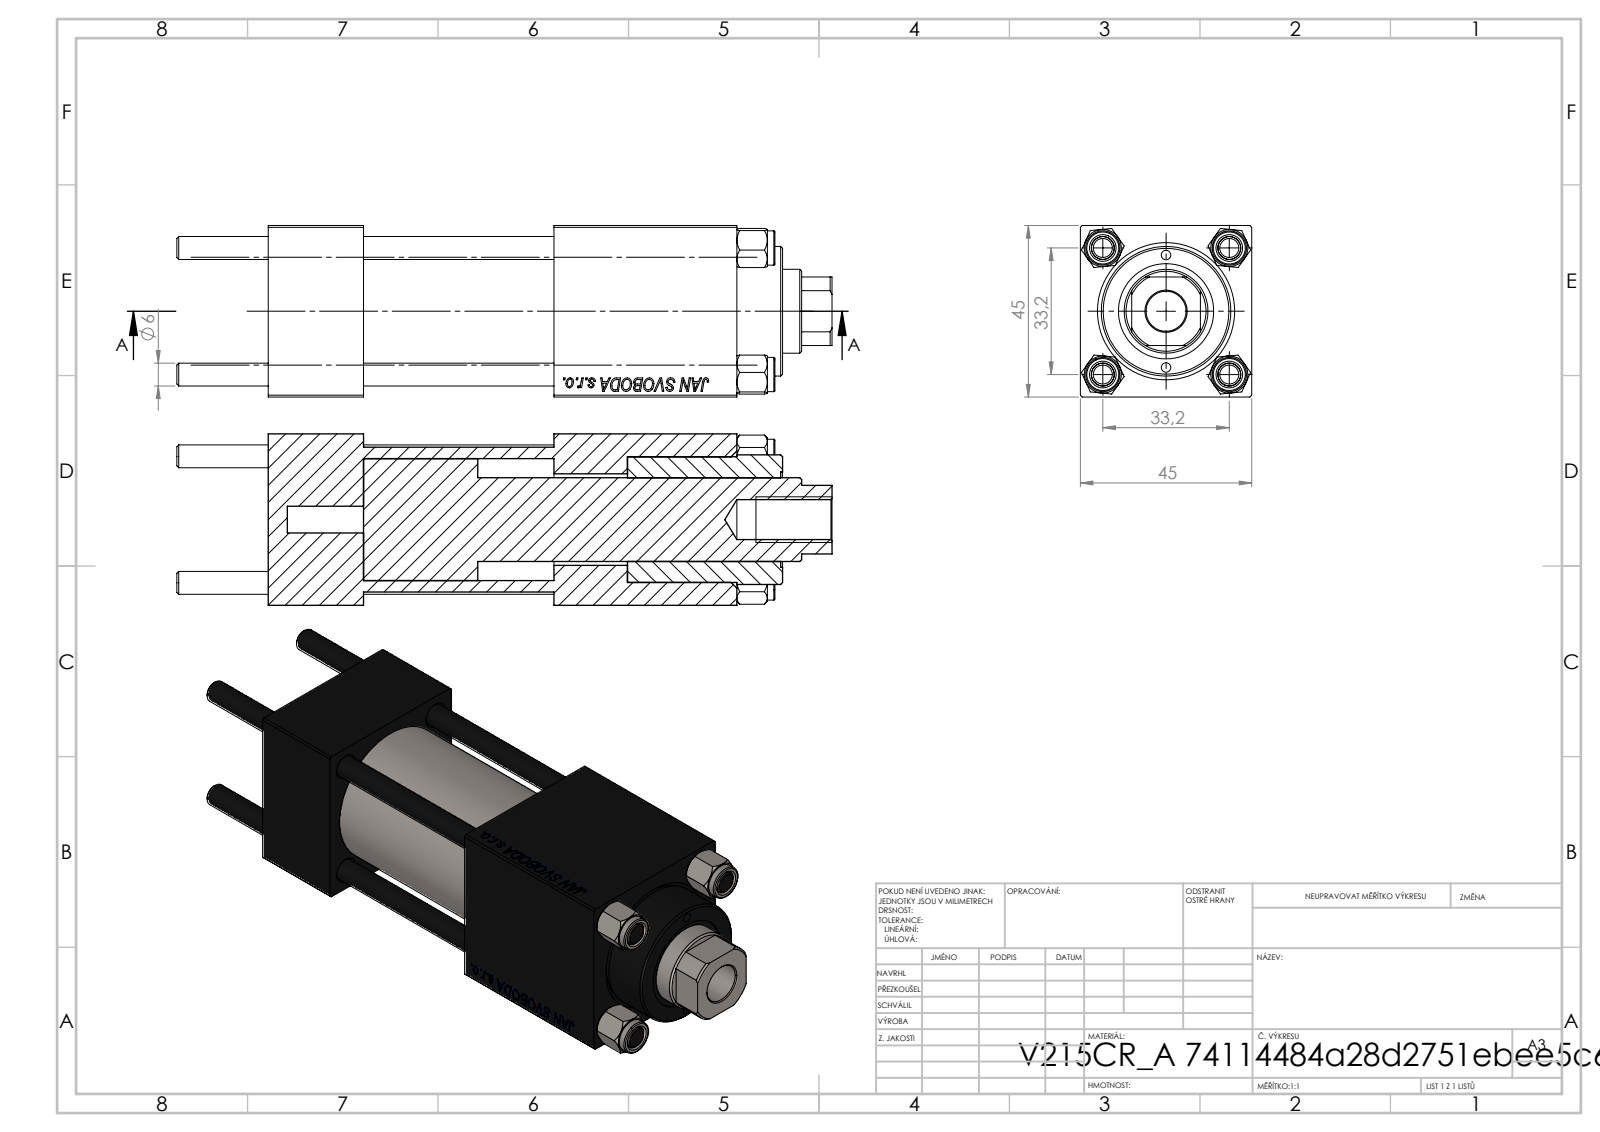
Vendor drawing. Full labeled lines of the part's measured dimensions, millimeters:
Part name (STEP PRODUCT): CR025_012_A_0_G_A_G_M_020_+#_##_TYCINKA; V215CR_BODY_A; NUT_M5; V215_VC_A (+1 more)
STEP written by: SolidWorks 2019 (CONFIG_CONTROL_DESIGN)
Units: millimetres
Bodies: 11 solids, 1139 faces (521 planar, 82 cylindrical, 536 other)
Overall size (bounding box): 172 × 45 × 45
Volume: 214 107 mm³ · Surface area: 77 308 mm²
Round holes (diameter × count): ⌀6 ×4, ⌀2.5 ×2, ⌀7 ×2, ⌀13.16 ×2, ⌀20 ×2, ⌀10.5 ×1, ⌀22 ×1, ⌀24 ×1, ⌀25 ×1, ⌀32 ×1, ⌀33 ×1
Round bosses / shafts (diameter × count): ⌀9 ×4, ⌀38 ×1, ⌀34 ×1
Partial cylindrical surfaces — rounded edges, fillets, slot ends (radius × count): R10.5 ×1
Main face-to-face distances: 45, 25, 123, 50, 75, 98, 48, 94.3, 69.3, 19.3
Hole centre spacings: 16.7, 23.48, 33.2, 35.47, 14.75, 46.95, 29.5, 75.5
